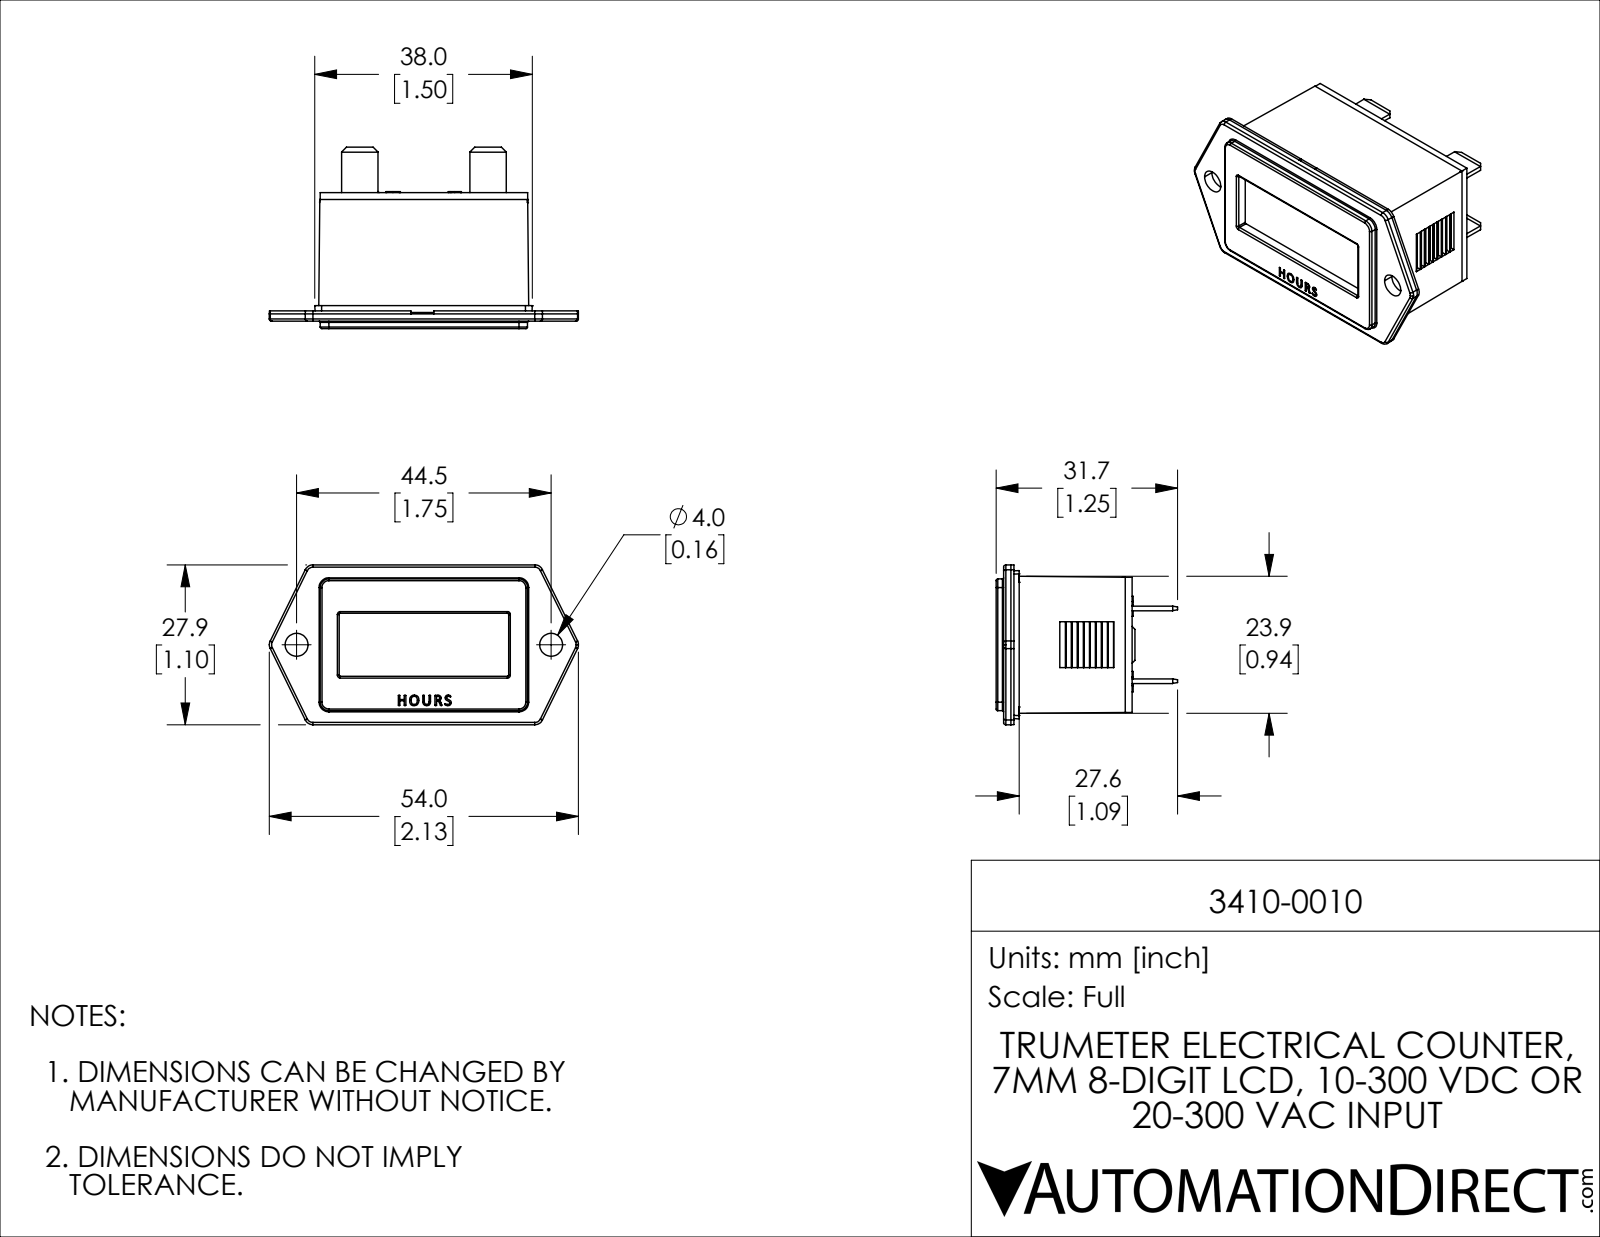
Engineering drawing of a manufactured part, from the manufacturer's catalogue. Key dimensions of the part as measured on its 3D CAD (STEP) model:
Part name (STEP PRODUCT): 3410-0010
STEP written by: SolidWorks 2021 (CONFIG_CONTROL_DESIGN)
Units: millimetres
Bodies: 2 solids, 618 faces (374 planar, 103 cylindrical, 141 other)
Overall size (bounding box): 53.98 × 31.68 × 27.9
Volume: 19 805 mm³ · Surface area: 9 276 mm²
Round holes (diameter × count): ⌀4 ×2
Partial cylindrical surfaces — rounded edges, fillets, slot ends (radius × count): R1.5 ×14, R0.2 ×8, R0.3 ×8, R0.25 ×6, R0.4 ×6, R0.76 ×4, R0.14 ×2, R0.25 ×2
Main face-to-face distances: 0.94, 20.9, 1.2, 21.84, 20.64, 20.61, 1.23, 19.67, 19.7, 0.8
Hole centre spacings: 44.46
